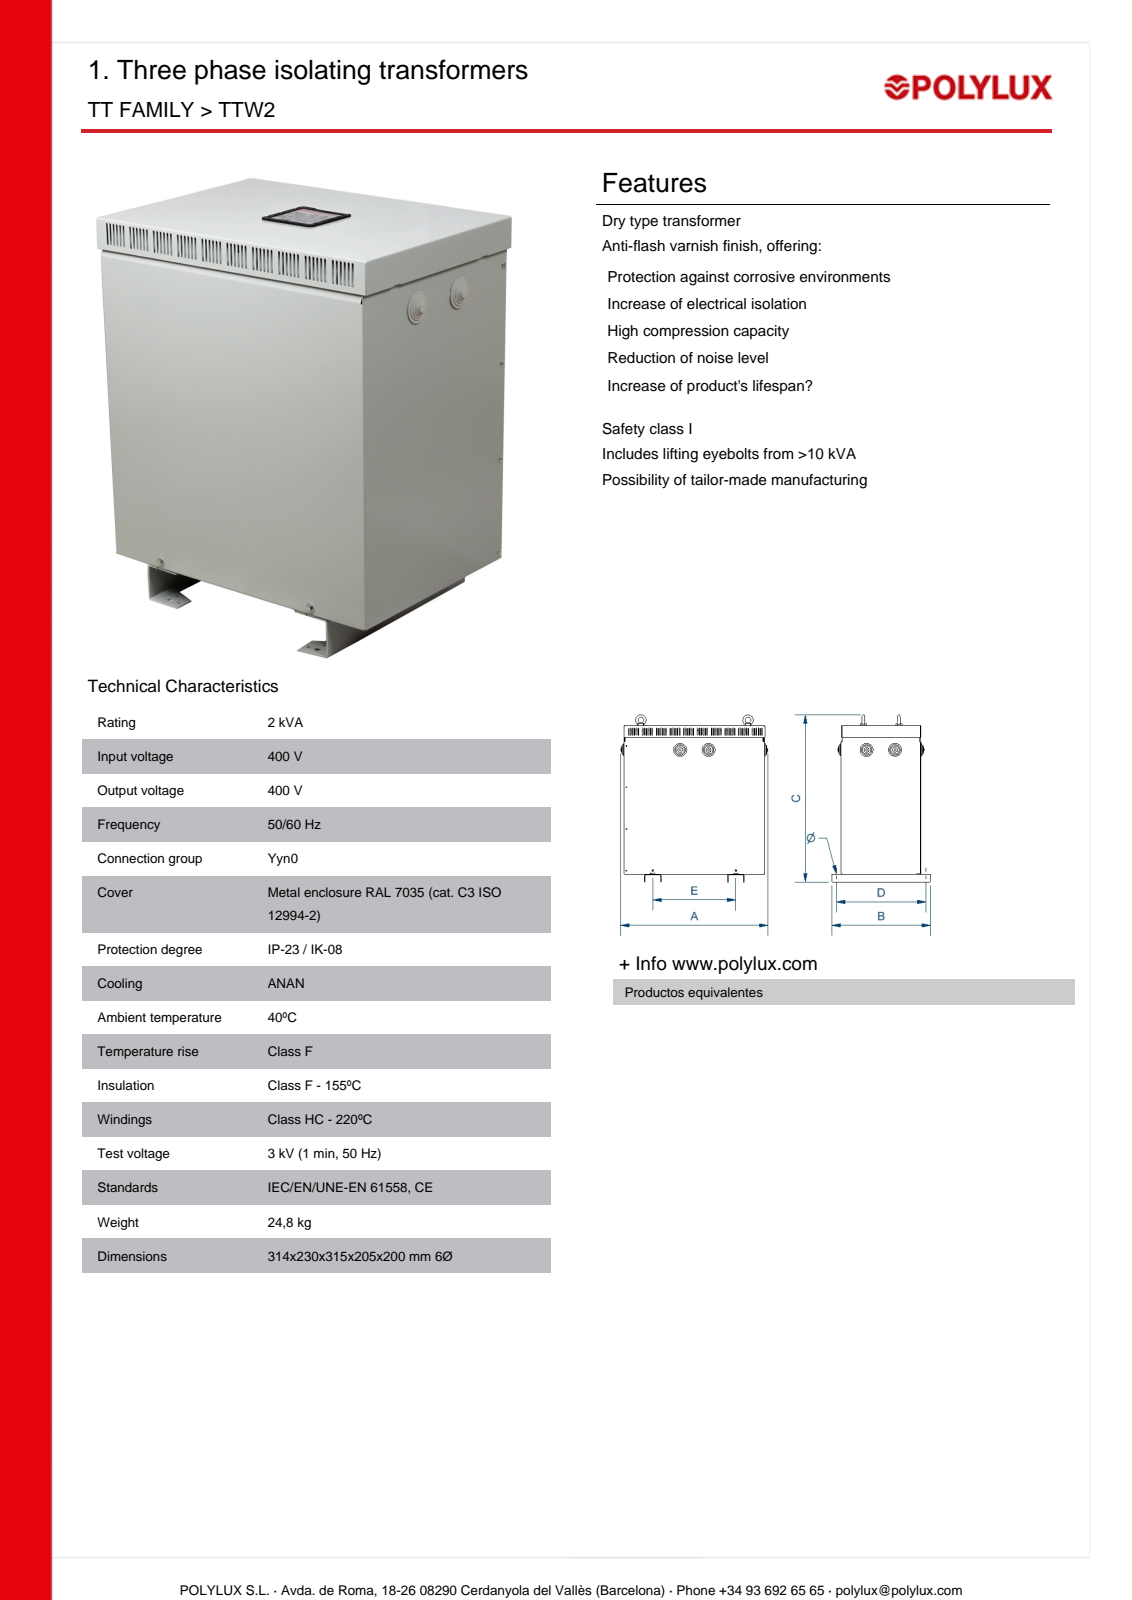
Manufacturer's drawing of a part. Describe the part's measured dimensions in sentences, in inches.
The part is named "CAJ08C23". Its 3-D file was written by "Autodesk Inventor 2018 (AUTOMOTIVE_DESIGN)". It is 12 solids with 876 faces: 662 planar, 128 cylindrical and 86 other. Overall it measures 12.569 by 12.295 by 9.055 inches. Its volume is 40.41 cubic inches and its surface area 1 297 square inches. Round holes: 5 of diameter 0.197, 4 of diameter 0.236, 3 of diameter 0.138, 2 of diameter 0.118, 2 of diameter 0.157, 2 of diameter 0.906, 2 of diameter 0.984. Round bosses or shafts: 2 of diameter 1.358, 2 of diameter 1.299, 2 of diameter 1.138, 2 of diameter 1.094, 2 of diameter 1.047, 2 of diameter 0.858, 2 of diameter 0.76, 2 of diameter 0.713. Partial cylindrical surfaces (rounded edges, fillets, slot ends): 20 of radius 0.079, 10 of radius 0.059, 10 of radius 0.118, 8 of radius 0.197, 6 of radius 0.157, 5 of radius 0.02, 4 of radius 0.098. The main face-to-face distances are 0.059, 7.48, 0.079, 12.146, 7.421, 7.539, 12.205, 12.087, 0.02, 11.634. The hole center spacings are 7.756, 2.047, 6.024, 8.022, 8.071, 9.033, 9.82, 10.147.
